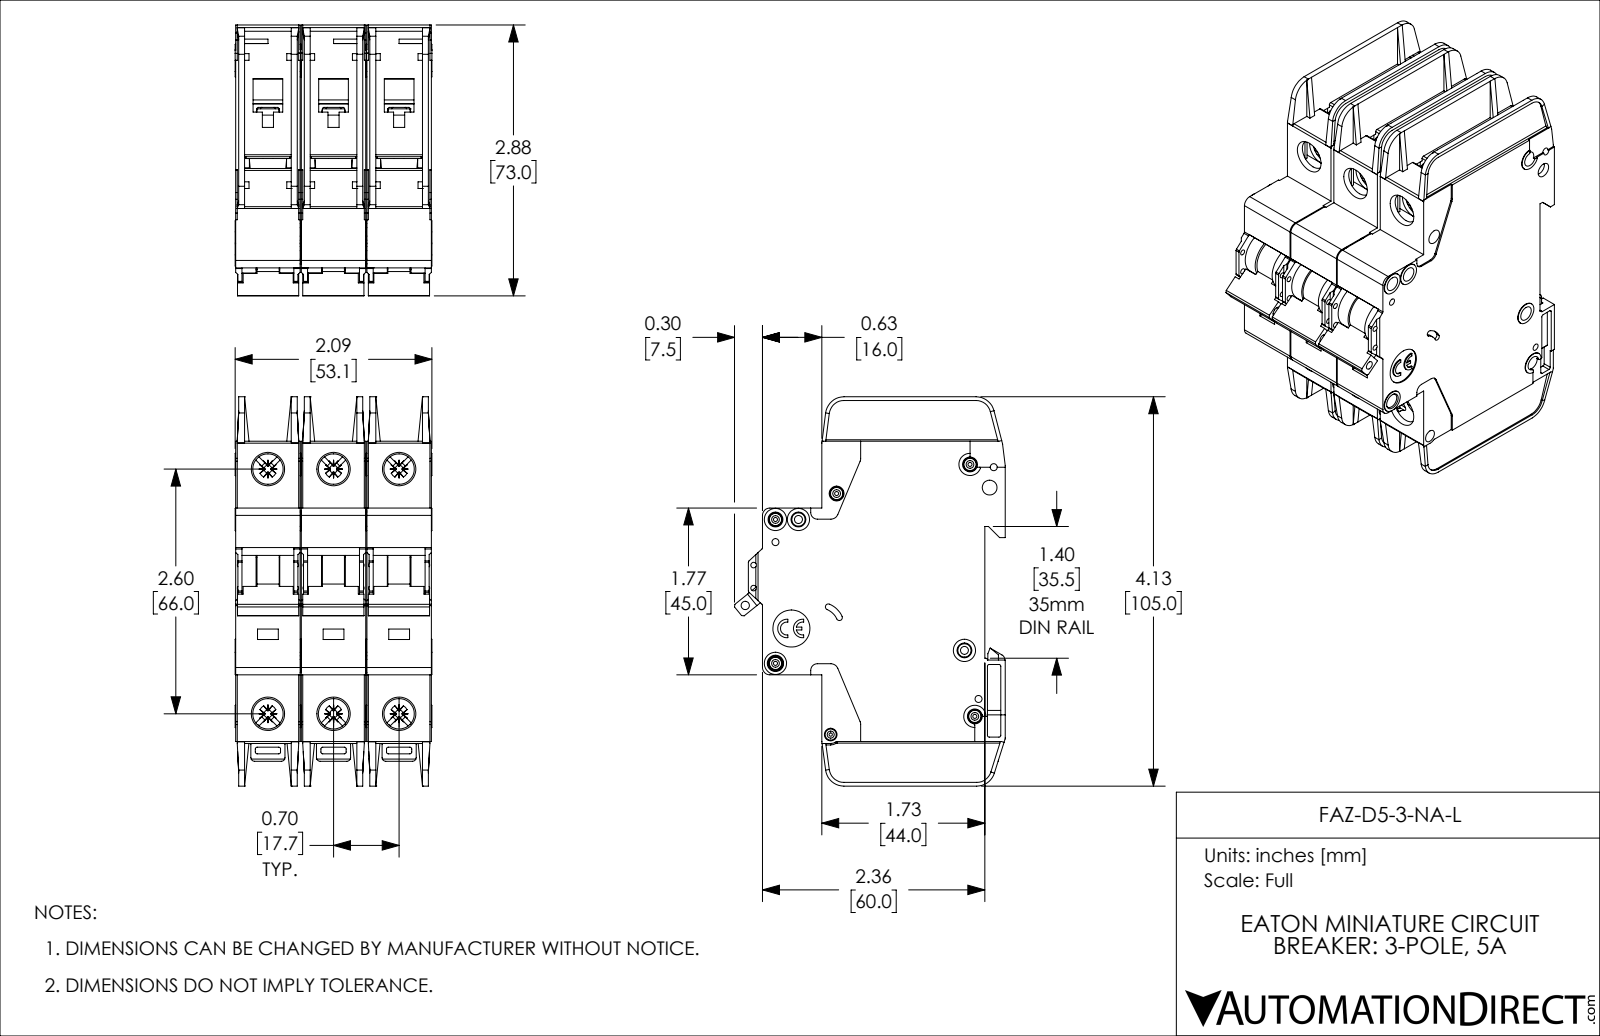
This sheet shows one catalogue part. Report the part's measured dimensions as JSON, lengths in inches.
{"part_name": "FAZ-D5-3-NA-L", "step_written_by": "SolidWorks 2019 (AUTOMOTIVE_DESIGN)", "units": "inches", "bodies": {"solids": 3, "faces": 3381, "planar": 2013, "cylindrical": 1071, "other": 297}, "overall_size": [4.134, 2.876, 2.091], "volume_in3": 14.05, "surface_area_in2": 123, "round_holes": [[0.157, 8], [0.323, 6], [0.043, 5], [0.075, 4], [0.059, 2], [0.085, 2], [0.035, 1], [0.089, 1], [0.098, 1], [0.134, 1], [0.394, 1]], "round_bosses_or_shafts": [[0.13, 5], [0.236, 4], [0.118, 4], [0.098, 3]], "partial_cylinders_radius": [[0.02, 72], [0.016, 30], [0.039, 18], [0.043, 12], [0.079, 12], [0.008, 6], [0.01, 6], [0.028, 6]], "face_to_face_distances": [0.697, 0.047, 1.394, 0.685, 0.591, 1.382, 0.744, 0.65, 0.106, 0.094], "hole_center_spacings": [0.697, 2.69, 2.598, 0.244, 0.537, 0.87, 1.394, 2.948]}
